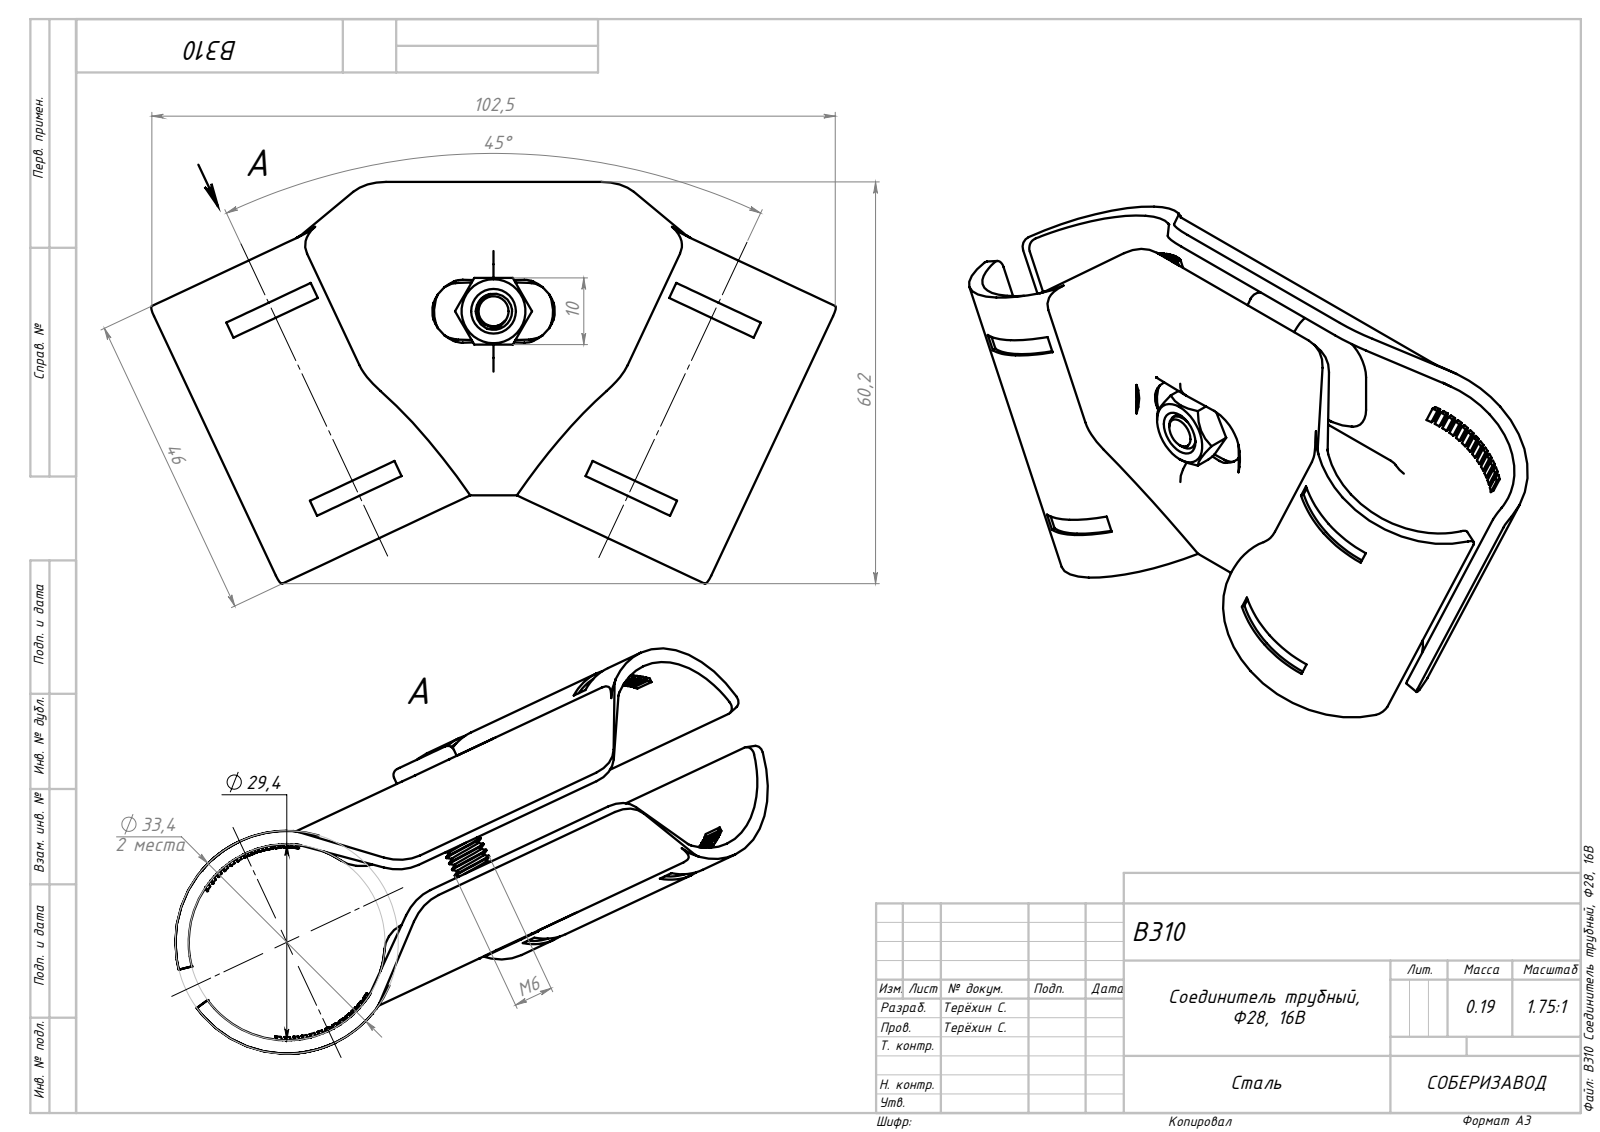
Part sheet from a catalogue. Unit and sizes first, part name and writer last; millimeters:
Units: millimetres
Overall size (bounding box): 102.7 × 60.26 × 33.42
Round holes (diameter × count): ⌀5.3 ×1, ⌀7.5 ×1
Round bosses / shafts (diameter × count): ⌀33.42 ×2, ⌀9.9 ×1, ⌀7 ×1, ⌀5.9 ×1
Partial cylindrical surfaces — rounded edges, fillets, slot ends (radius × count): R0.3 ×6, R3 ×4, R14.21 ×4, R14.71 ×4, R16.21 ×4, R5 ×2, R10 ×2
Main face-to-face distances: 2, 24.94, 26.94, 4, 22.94, 28.94, 20.94, 6, 18.94, 29.5
Bodies: 0 solids, 941 faces (502 planar, 196 cylindrical, 243 other)
Part name (STEP PRODUCT): B310 Соединитель трубный, Ф28, 16B
STEP written by: SolidWorks 2022 (AUTOMOTIVE_DESIGN)
